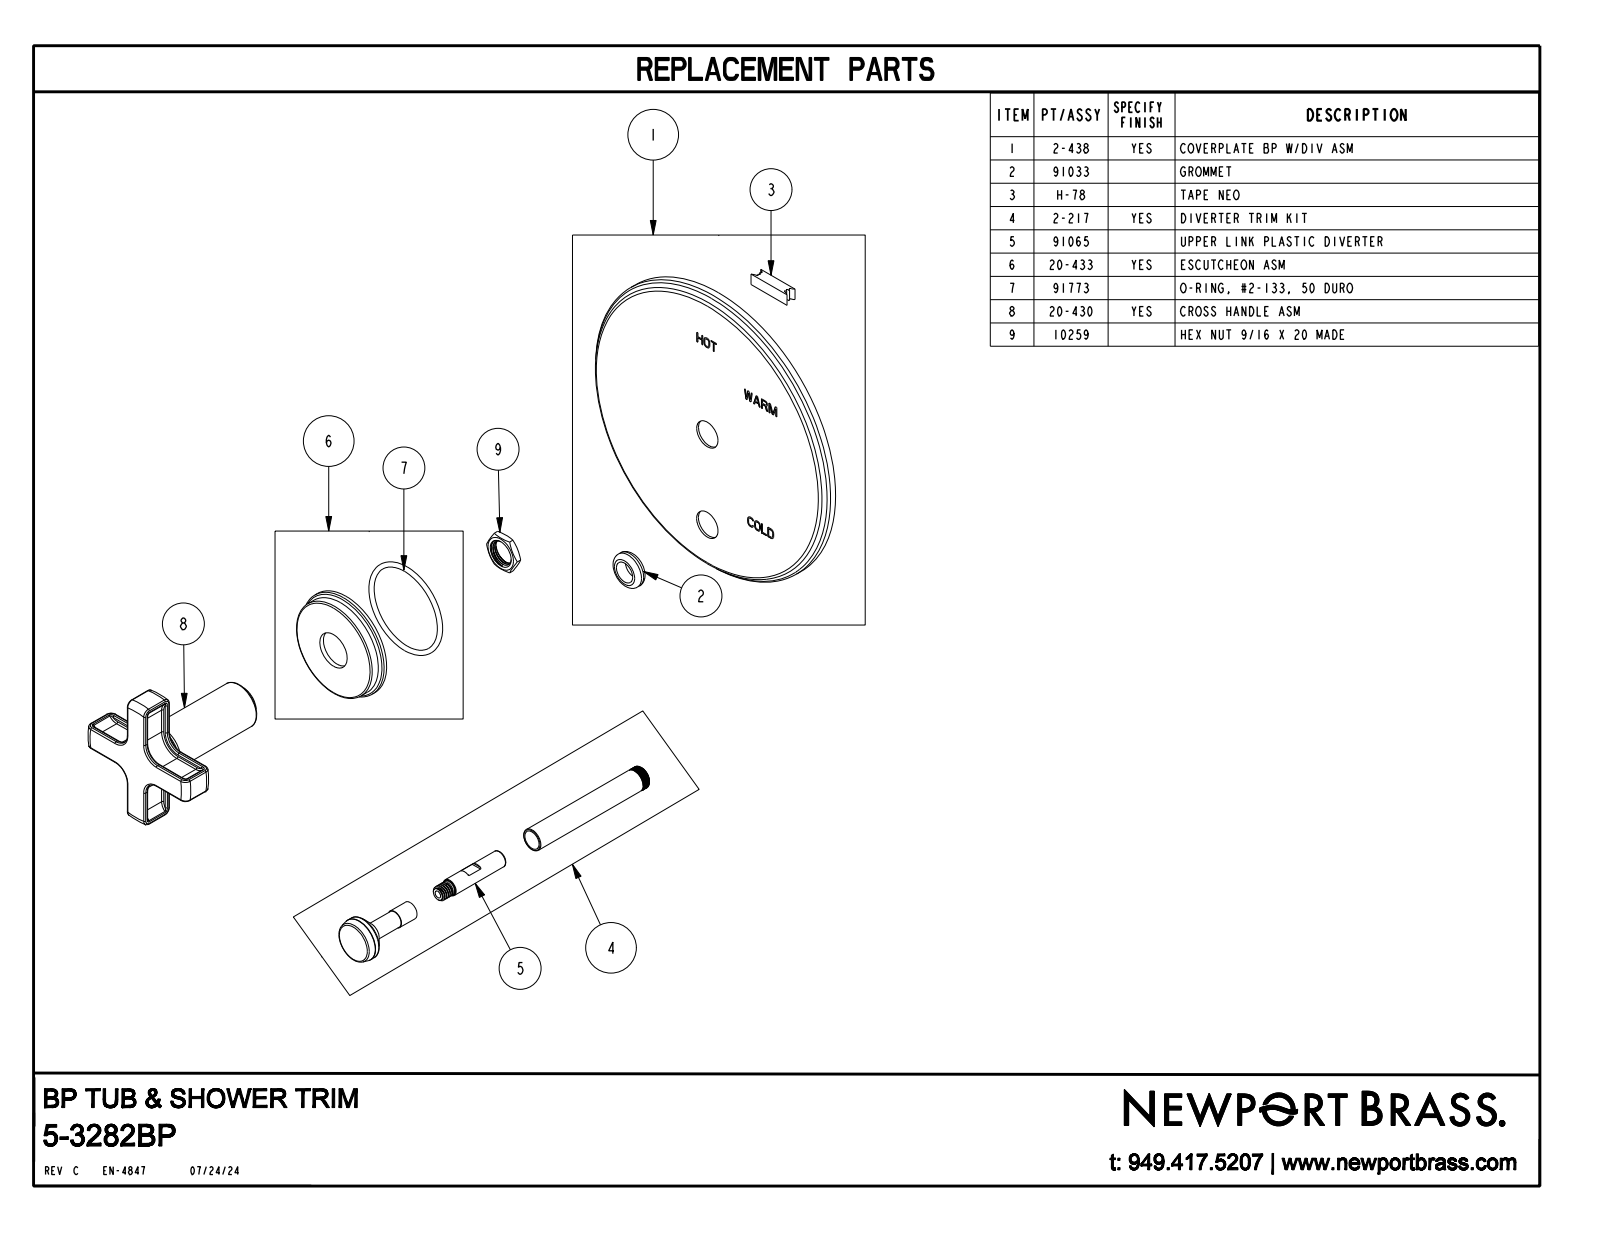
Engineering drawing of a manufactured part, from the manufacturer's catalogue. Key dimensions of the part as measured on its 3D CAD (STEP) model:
Part name (STEP PRODUCT): 11118_AF3; 91033; H-78; 2-438_AF3_ASM (+8 more)
STEP written by: CREO PARAMETRIC BY PTC INC, 2018400 (CONFIG_CONTROL_DESIGN)
Units: inches
Bodies: 17 solids, 1421 faces (496 planar, 534 cylindrical, 391 other)
Overall size (bounding box): 6.5 × 6.5 × 6.101
Volume: 5.664 in³ · Surface area: 202.9 in²
Round holes (diameter × count): ⌀0.11 ×1, ⌀0.15 ×1, ⌀0.168 ×1, ⌀0.265 ×1, ⌀0.275 ×1, ⌀0.318 ×1, ⌀0.345 ×1, ⌀0.358 ×1, ⌀0.36 ×1, ⌀0.375 ×1, ⌀0.383 ×1, ⌀0.397 ×1
Round bosses / shafts (diameter × count): ⌀6.5 ×1, ⌀2.25 ×1, ⌀2.09 ×1, ⌀1.812 ×1, ⌀0.975 ×1, ⌀0.9 ×1, ⌀0.85 ×1, ⌀0.73 ×1
Partial cylindrical surfaces — rounded edges, fillets, slot ends (radius × count): R0.03 ×40, R0.25 ×8, R0.01 ×6, R0.042 ×6, R0.325 ×4, R0.425 ×4, R0.072 ×1, R0.137 ×1
Main face-to-face distances: 0.05, 0.4, 0.35, 2.901, 3.301, 3.251, 0.1, 0.7, 2.601, 2.551
Hole centre spacings: 2.17
